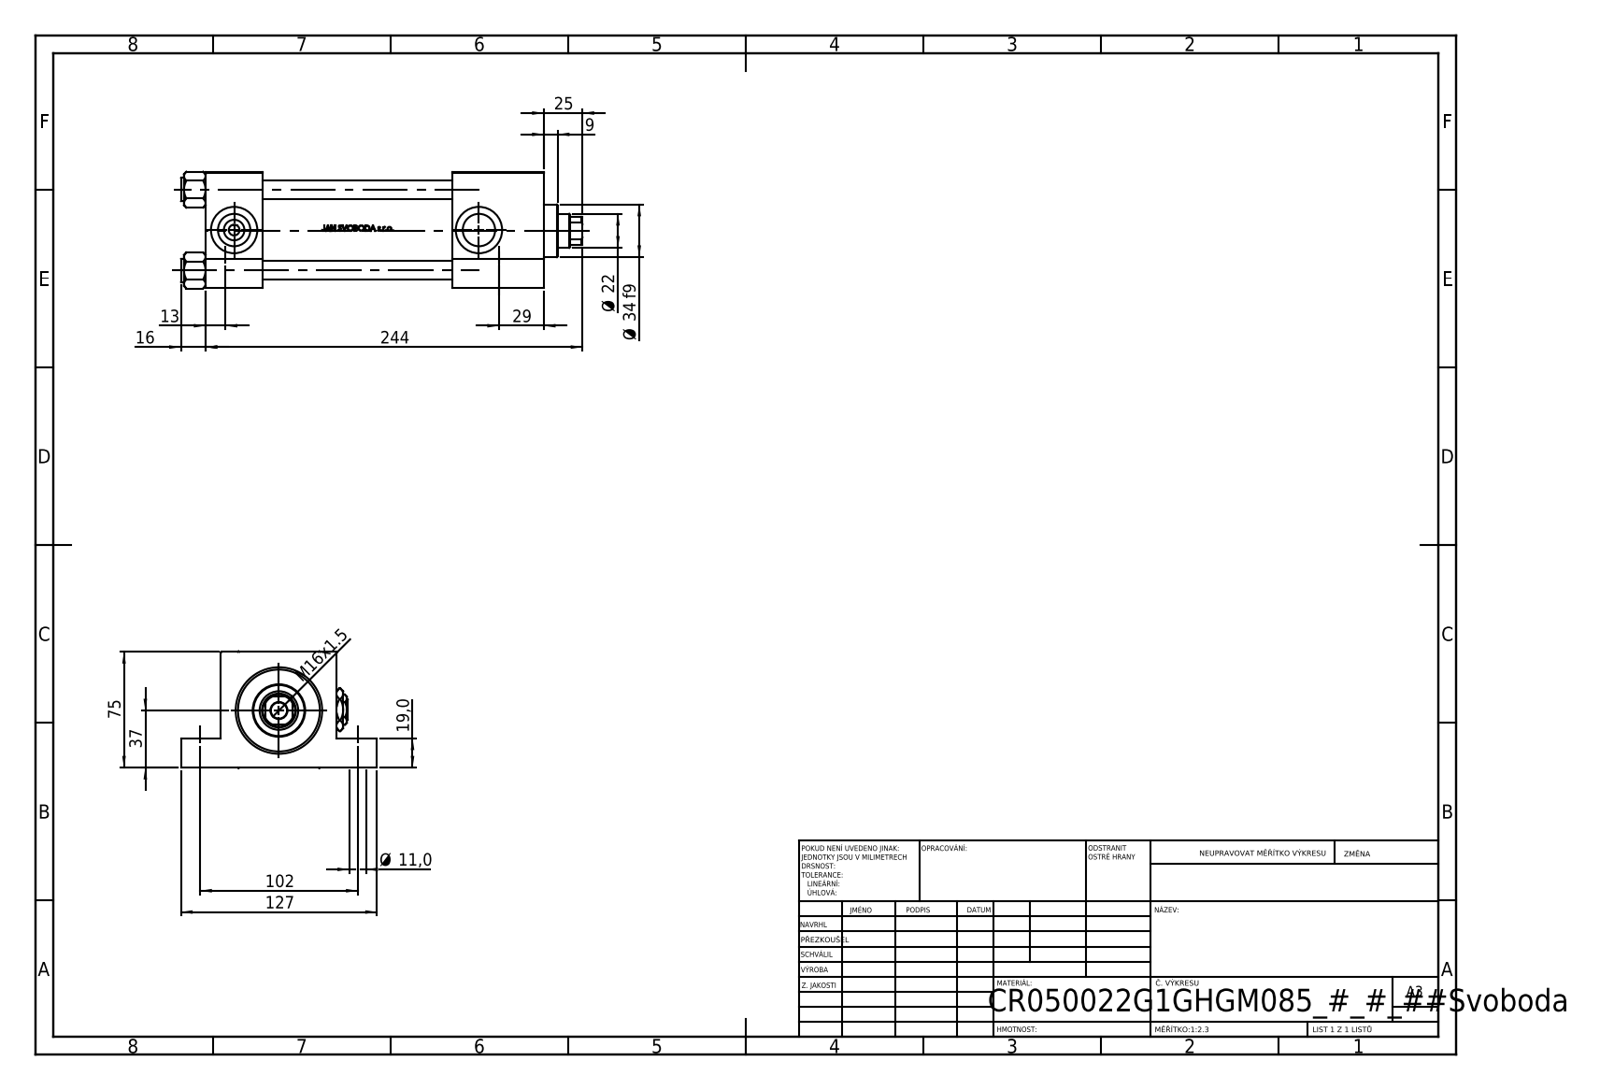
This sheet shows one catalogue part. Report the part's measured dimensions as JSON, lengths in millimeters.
{"part_name": "NUT_M5_G; V215_VC_A; V215CR_G_TYCINKA; V215CR_G_Body (+2 more)", "step_written_by": "SolidWorks 2019 (CONFIG_CONTROL_DESIGN)", "units": "millimeters", "bodies": {"solids": 12, "faces": 1134, "planar": 454, "cylindrical": 128, "other": 552}, "overall_size": [260, 127, 75.54], "volume_mm3": 838985, "surface_area_mm2": 197243, "round_holes": [[11, 4], [12, 4], [7, 2], [20.96, 2], [30, 2], [10.5, 1], [22, 1], [25, 1], [41, 1], [50, 1], [53, 1]], "round_bosses_or_shafts": [[15, 4], [56, 1], [34, 1]], "partial_cylinders_radius": [[10.5, 1]], "face_to_face_distances": [75, 37, 219, 182, 19, 56, 160, 123, 59, 26], "hole_center_spacings": [52.3, 36.63, 37.34, 73.96, 102, 177, 204.29, 158.5]}
